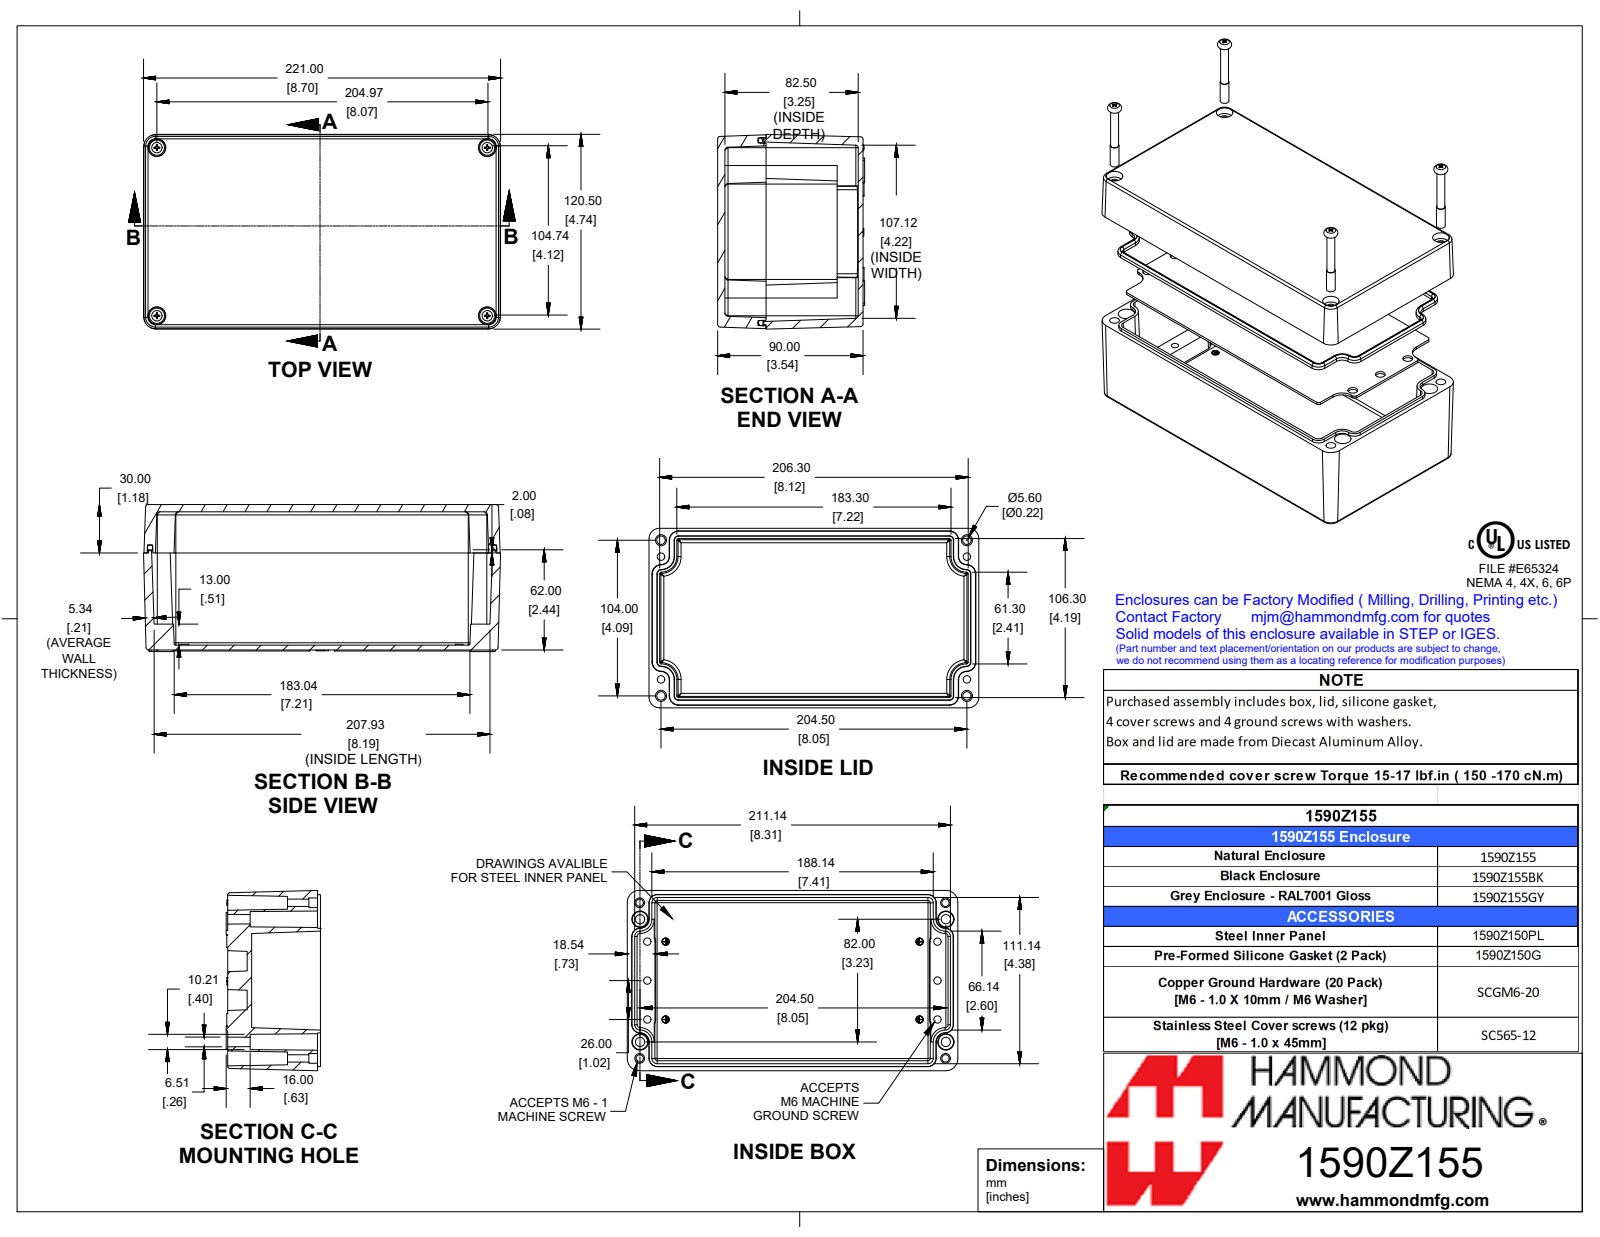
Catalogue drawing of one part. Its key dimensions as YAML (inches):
part_name: "1590Z155"
step_written_by: "SolidWorks 2019 (CONFIG_CONTROL_DESIGN)"
units: inches
bodies: {solids: 8, faces: 702, planar: 364, cylindrical: 80, other: 258}
overall_size: [8.701, 4.744, 3.583]
volume: 35.58
surface_area: 455.3
round_holes:
  - {diameter: 0.194, count: 10}
  - {diameter: 0.257, count: 6}
  - {diameter: 0.197, count: 4}
  - {diameter: 0.22, count: 4}
  - {diameter: 0.256, count: 4}
  - {diameter: 0.291, count: 4}
round_bosses_or_shafts:
  - {diameter: 0.231, count: 4}
  - {diameter: 0.208, count: 4}
partial_cylinders:
  - {radius: 0.059, count: 24}
  - {radius: 0.079, count: 6}
  - {radius: 0.34, count: 4}
face_to_face_distances: [3.543, 0.079, 0.63, 2.913, 0.187, 0.709, 0.118, 2.835, 3.366, 2.736]
hole_center_spacings: [1.024, 1.024, 7.638, 0.433, 0.625, 1.044, 1.627, 2.048]
